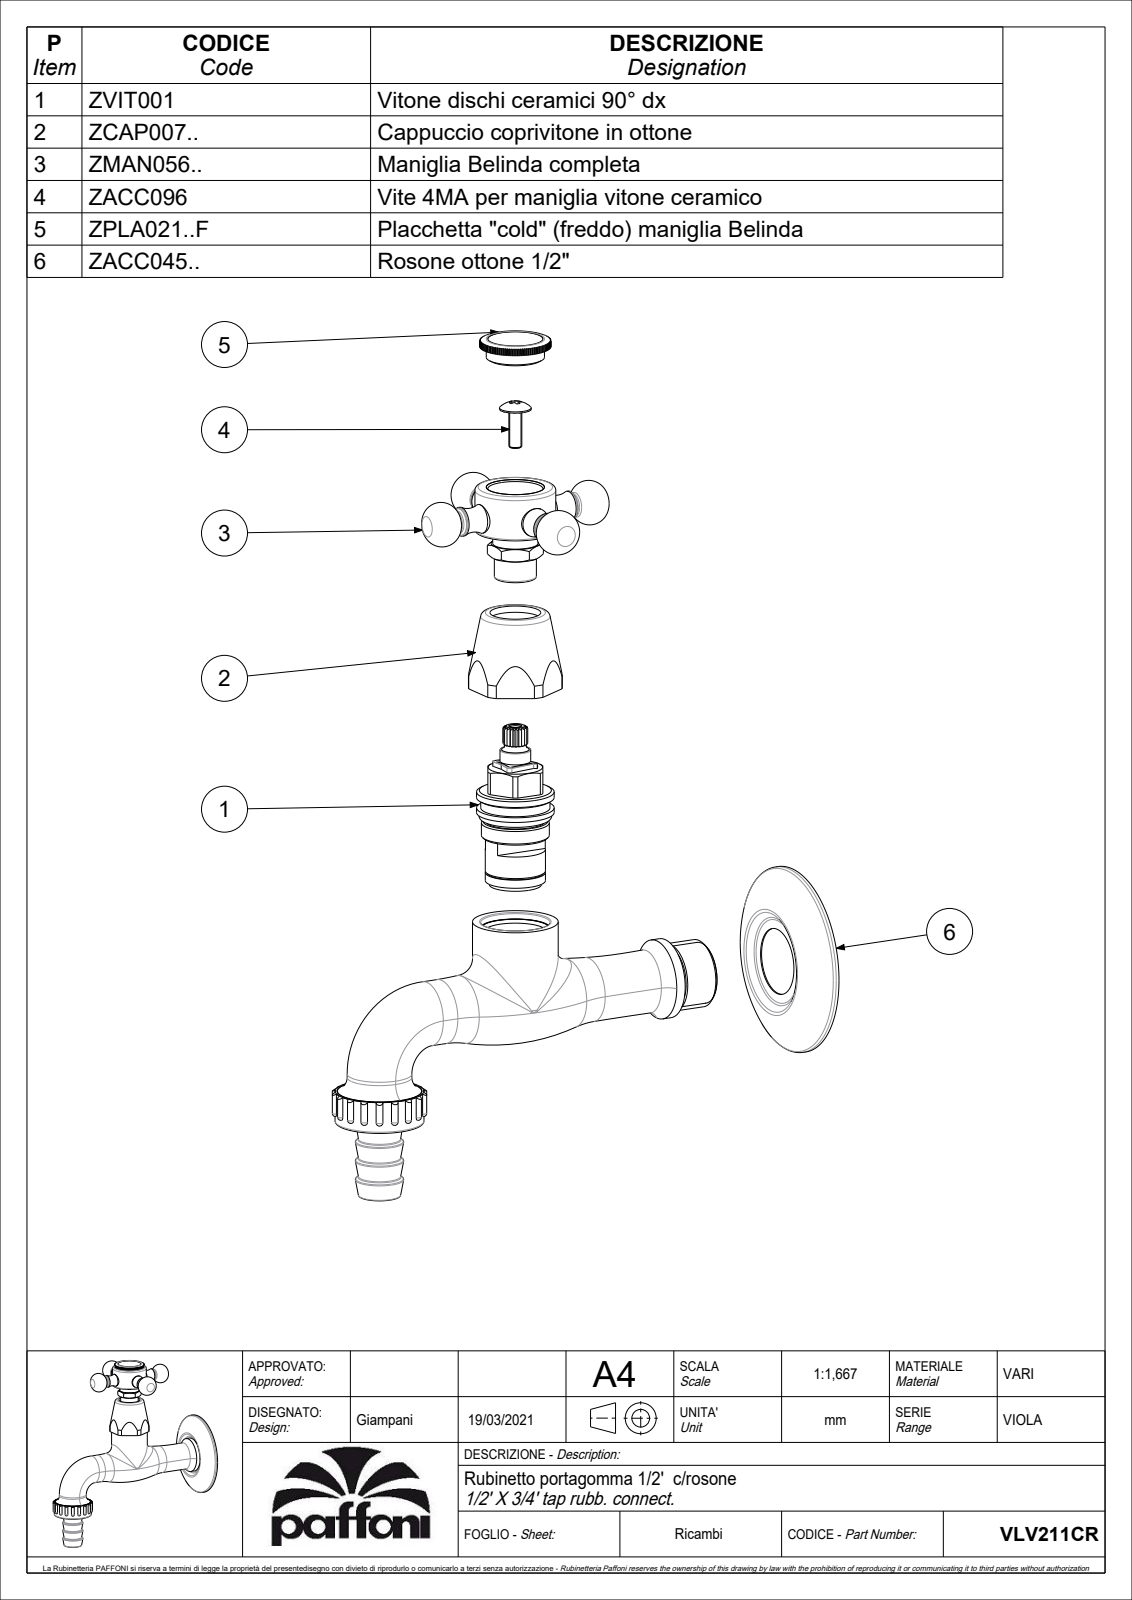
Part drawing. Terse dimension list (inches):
name: VLV211CR
written by: CREO PARAMETRIC BY PTC INC, 2020044 (CONFIG_CONTROL_DESIGN)
unit: in
bodies: 1 solid, 577 faces (234 planar, 166 cylindrical, 177 other)
size: 5.242 × 5.11 × 2.522
volume: 6.464 in³; area: 39.01 in²
bosses: 2× ⌀0.354, 2× ⌀0.276, 1× ⌀2.283, 1× ⌀1.083, 1× ⌀1.043, 1× ⌀0.984, 1× ⌀0.972, 1× ⌀0.827
rounds: 18× R0.041, 1× R0.433, 1× R0.571
face distances: 3.659, 1.043, 0.303, 0.226, 0.817, 3.219, 0.441, 0.925, 4.143, 4.584
